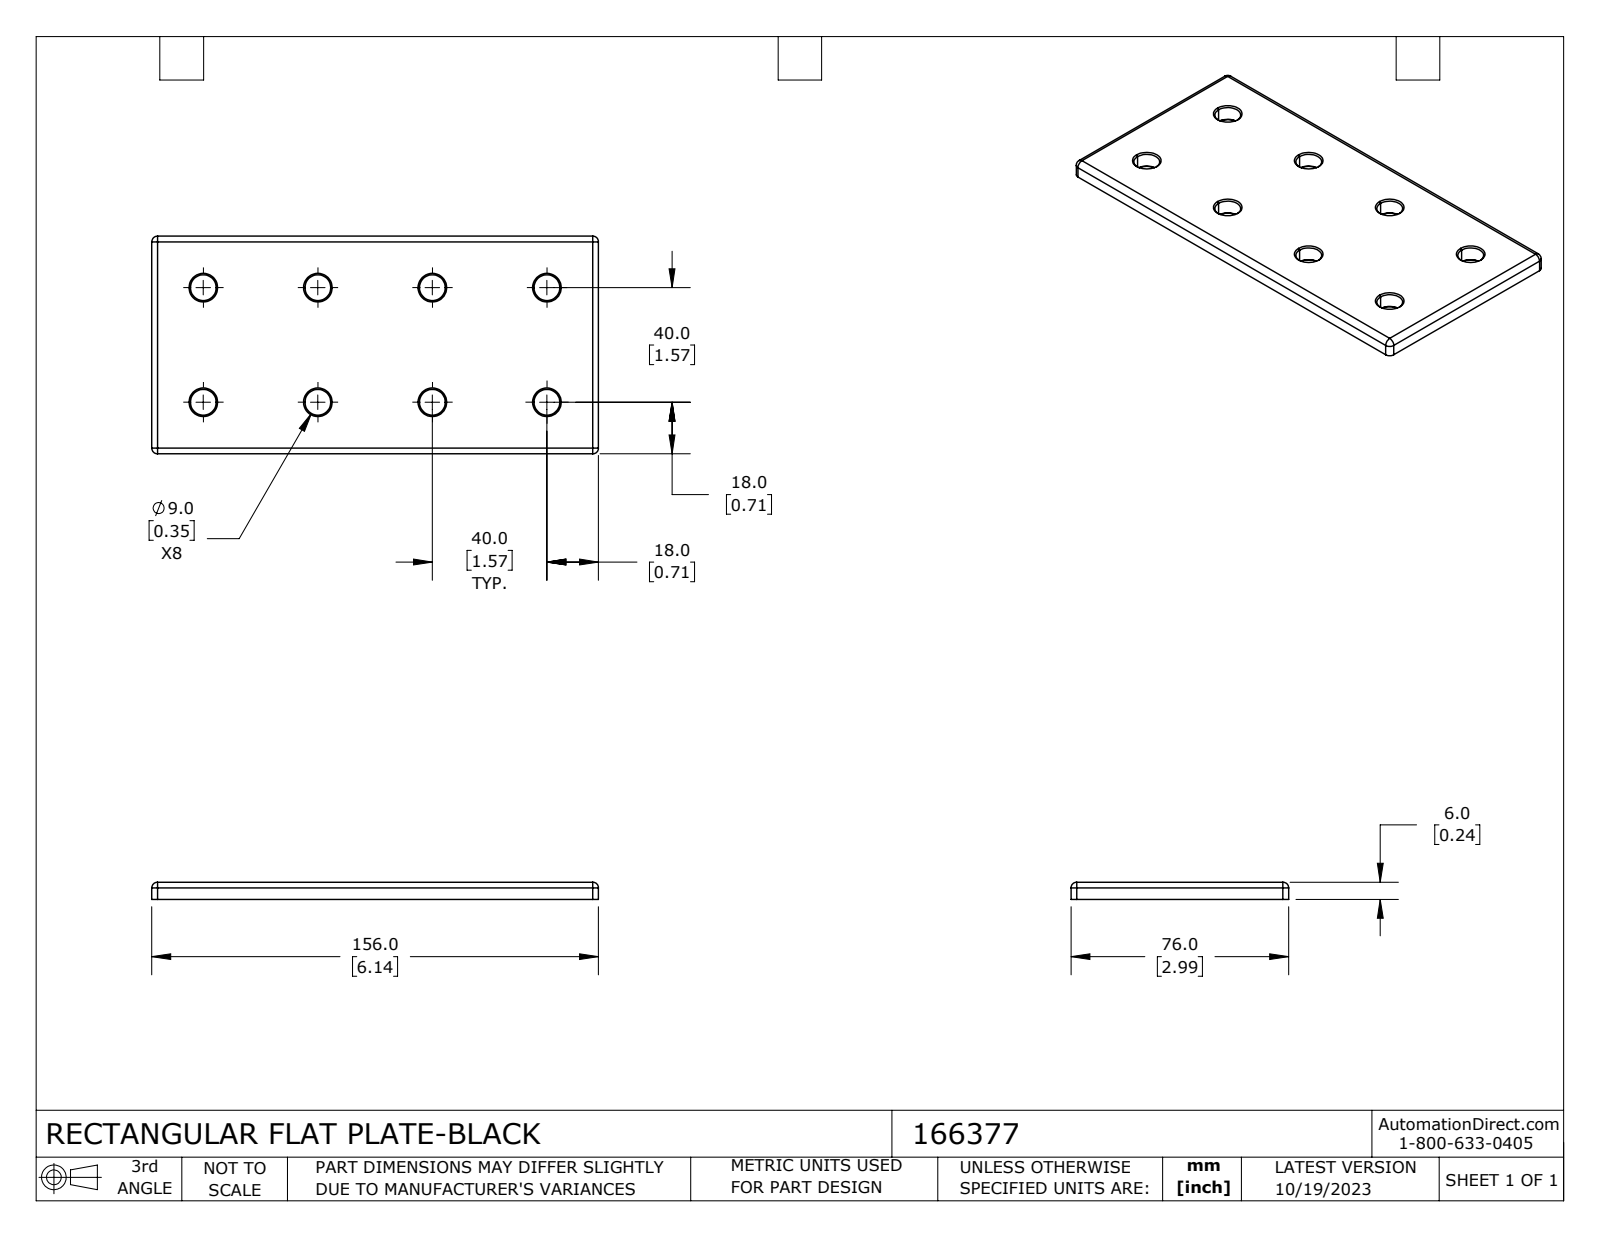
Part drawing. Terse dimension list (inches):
name: 166377
written by: SolidWorks 2023 (CONFIG_CONTROL_DESIGN)
unit: in
bodies: 1 solid, 66 faces (6 planar, 24 cylindrical, 36 other)
size: 6.142 × 2.992 × 0.236
volume: 4.126 in³; area: 40.74 in²
holes: 8× ⌀0.354
rounds: 8× R0.079
face distances: 0.236, 2.992, 6.142
hole spacings: 1.575, 2.227, 3.15, 3.521, 4.724, 4.98
